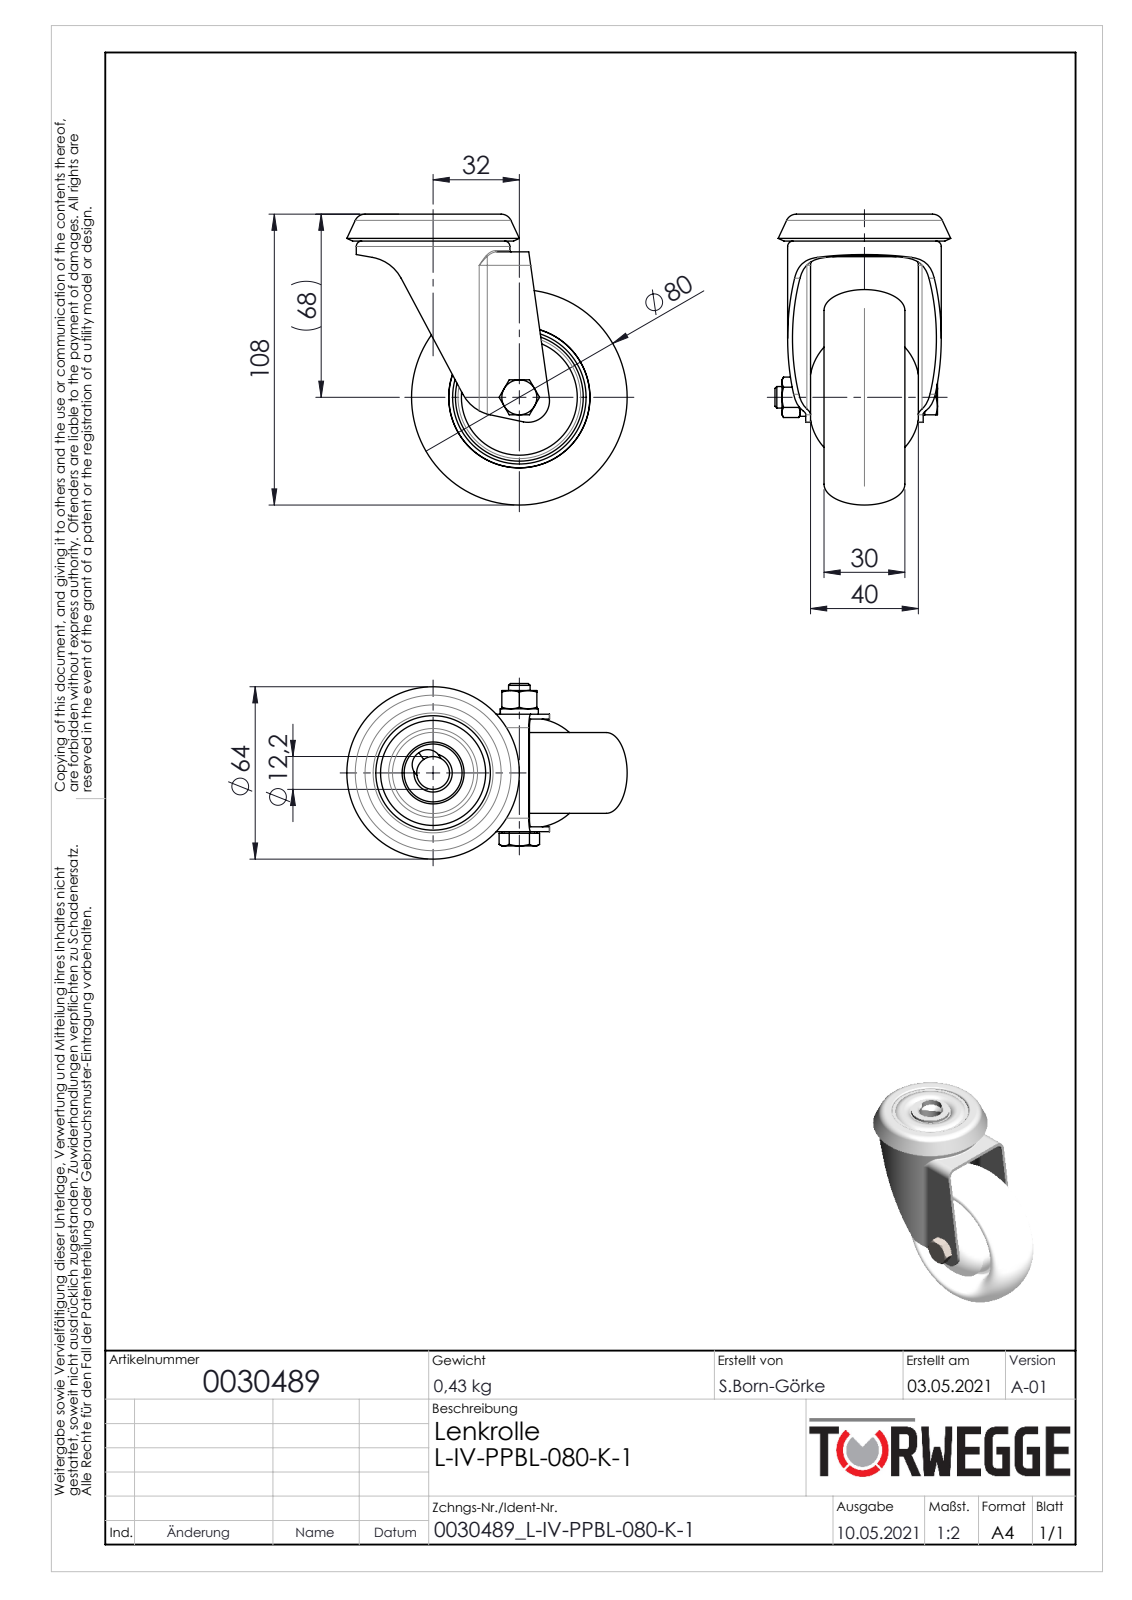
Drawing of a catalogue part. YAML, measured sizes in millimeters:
part_name: "0030489"
step_written_by: "SolidWorks 2020 (AUTOMOTIVE_DESIGN)"
units: millimeters
bodies: {solids: 8, faces: 242, planar: 62, cylindrical: 56, other: 124}
overall_size: [107.69, 104, 65.2]
volume: 157108
surface_area: 69615
round_holes:
  - {diameter: 6.8, count: 1}
  - {diameter: 8, count: 1}
  - {diameter: 8.1, count: 1}
  - {diameter: 8.3, count: 1}
  - {diameter: 12.2, count: 1}
  - {diameter: 33, count: 1}
  - {diameter: 35, count: 1}
  - {diameter: 53.4, count: 1}
round_bosses_or_shafts:
  - {diameter: 57, count: 1}
  - {diameter: 29, count: 1}
  - {diameter: 21.5, count: 1}
  - {diameter: 15, count: 1}
  - {diameter: 14.1, count: 1}
  - {diameter: 13, count: 1}
partial_cylinders:
  - {radius: 5, count: 4}
  - {radius: 3.2, count: 2}
  - {radius: 5.25, count: 2}
  - {radius: 6.8, count: 2}
  - {radius: 15, count: 2}
  - {radius: 8, count: 1}
face_to_face_distances: [1.8, 41.8, 8.5, 10.05, 33.55, 8.25, 31.75, 40, 43.6, 10.3]
